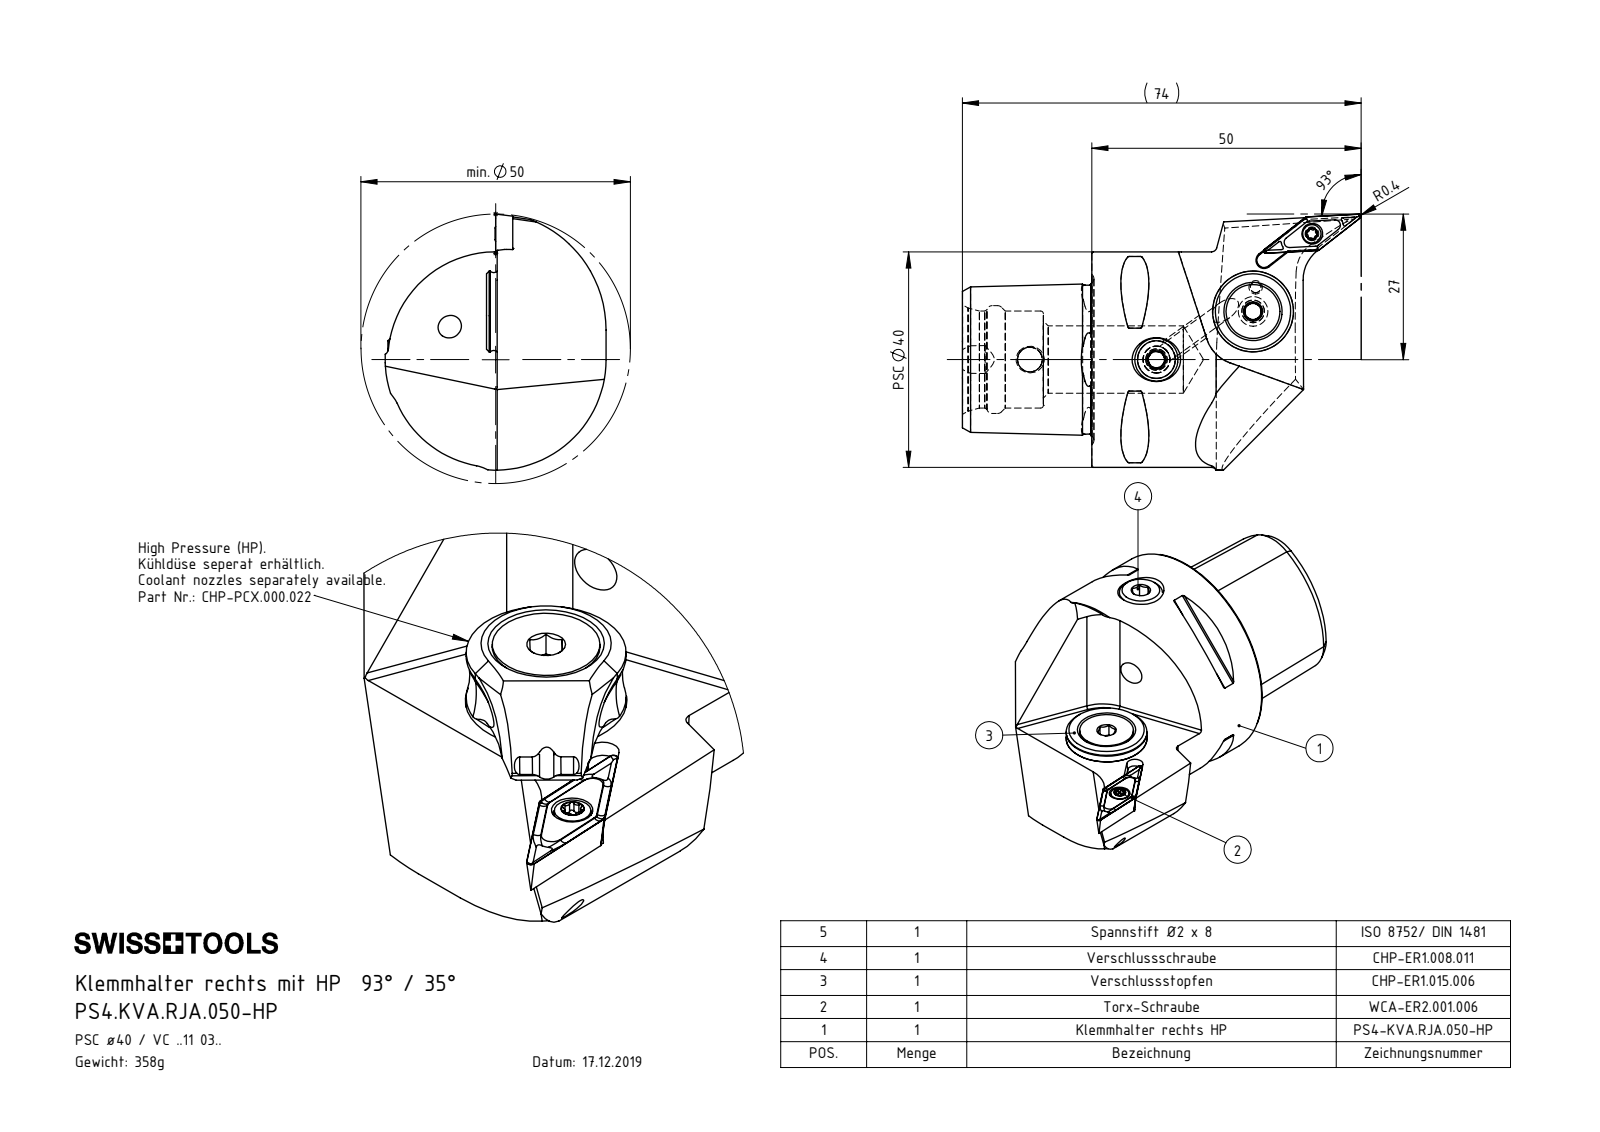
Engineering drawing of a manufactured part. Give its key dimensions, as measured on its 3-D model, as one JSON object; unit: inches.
{"part_name": "VCGT110304; CHP-ER1.015.006; CHP-ER1.008.011_A; DIN 7991 - M5x15 (+6 more)", "step_written_by": "SolidWorks 2017 (AUTOMOTIVE_DESIGN)", "units": "inches", "bodies": {"solids": 8, "faces": 278, "planar": 94, "cylindrical": 63, "other": 121}, "overall_size": [2.913, 1.87, 1.614], "volume_in3": 2.795, "surface_area_in2": 22.65, "round_holes": [[0.165, 2], [0.047, 1], [0.079, 1], [0.081, 1], [0.098, 1], [0.11, 1], [0.118, 1], [0.13, 1], [0.152, 1], [0.157, 1], [0.181, 1], [0.197, 1]], "round_bosses_or_shafts": [[1.575, 1], [0.591, 1], [0.528, 1], [0.394, 1], [0.315, 1], [0.217, 1], [0.197, 1], [0.134, 1]], "partial_cylinders_radius": [[0.012, 8], [0.008, 6], [0.014, 5], [0.02, 2], [0.276, 2], [0.014, 1], [0.053, 1], [0.118, 1]], "face_to_face_distances": [0.177, 0.945, 0.611, 0.064, 0.113, 0.618, 0.591, 1.39, 0.682, 0.795], "hole_center_spacings": [0.177, 0.567, 0.57, 0.711, 0.714, 0.789, 0.897, 0.925]}
